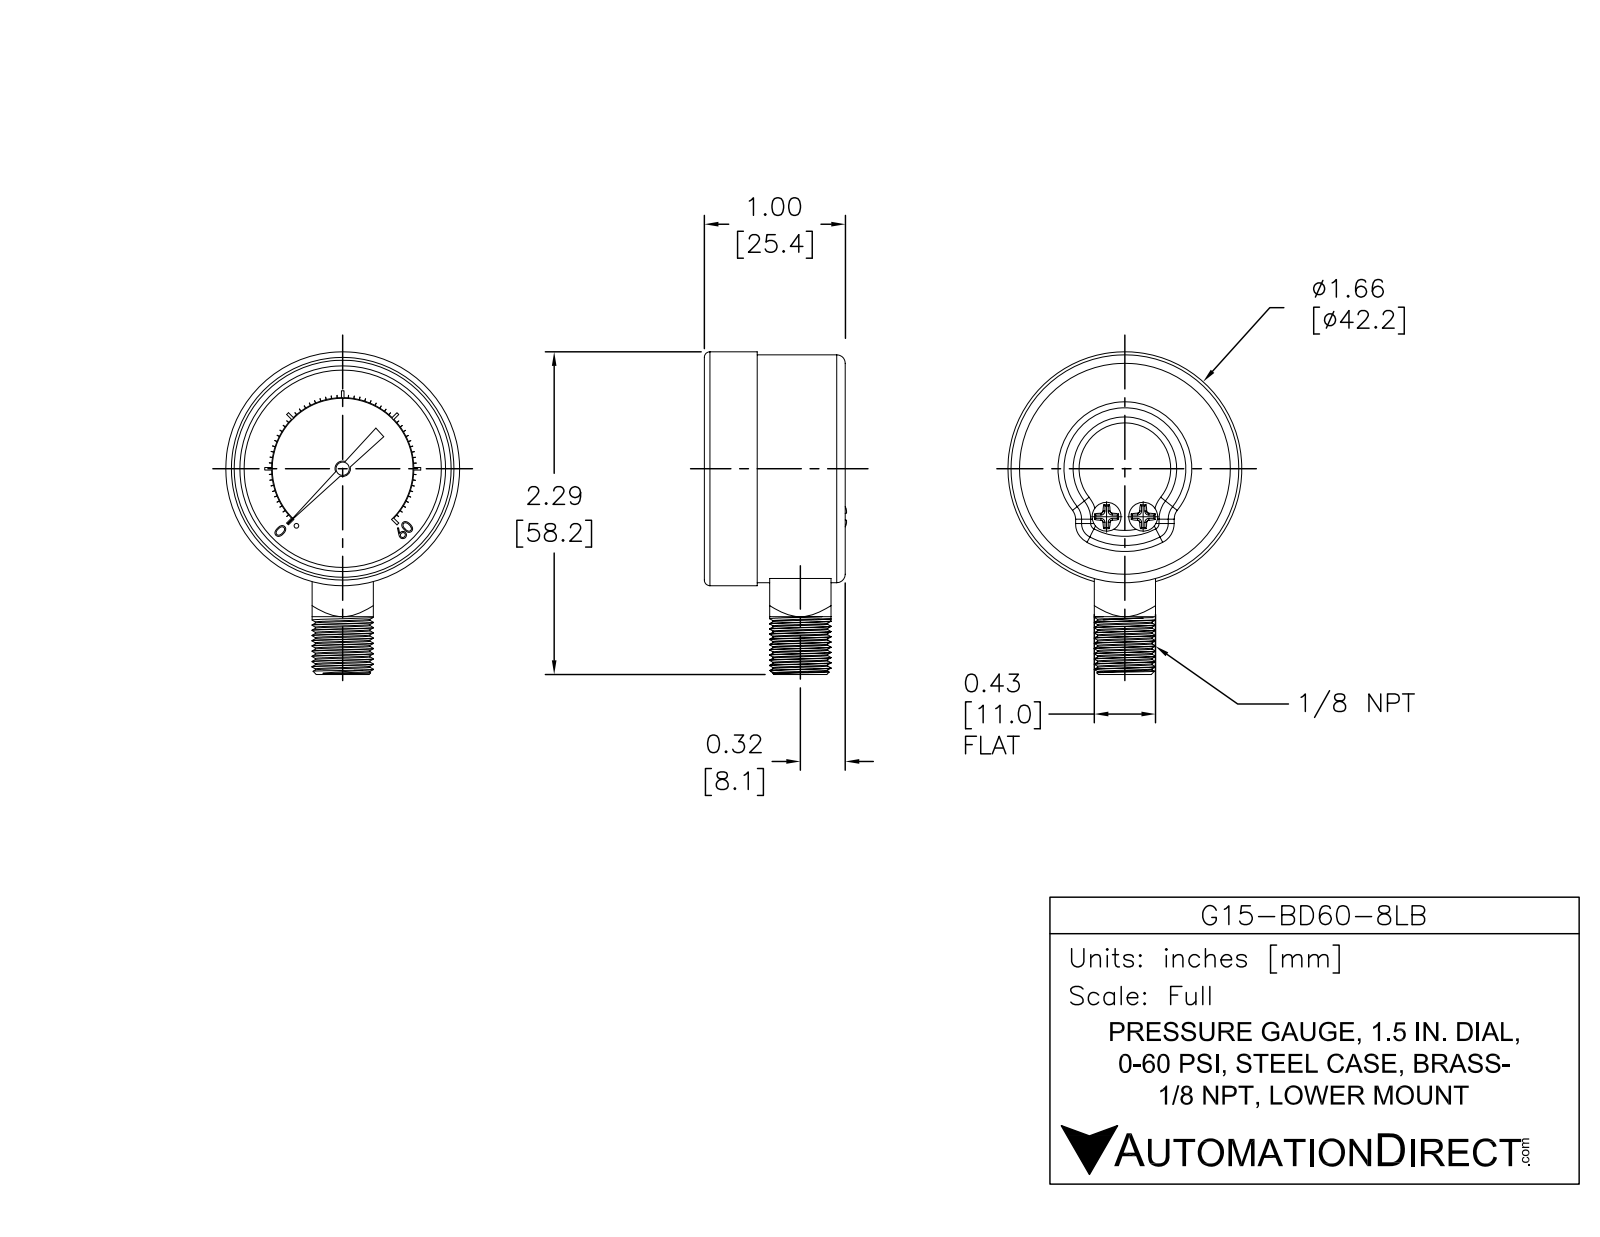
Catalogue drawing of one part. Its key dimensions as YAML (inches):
part_name: "G15-BD60-8LB"
step_written_by: "SolidWorks 2021 (AUTOMOTIVE_DESIGN)"
units: inches
bodies: {solids: 1, faces: 413, planar: 266, cylindrical: 82, other: 65}
overall_size: [2.29, 1.66, 1.01]
volume: 1.682
surface_area: 12.05
round_holes:
  - {diameter: 0.14, count: 1}
  - {diameter: 1.4, count: 1}
round_bosses_or_shafts:
  - {diameter: 0.205, count: 2}
  - {diameter: 1.66, count: 1}
  - {diameter: 1.617, count: 1}
  - {diameter: 0.435, count: 1}
  - {diameter: 0.11, count: 1}
  - {diameter: 0.095, count: 1}
  - {diameter: 0.033, count: 1}
partial_cylinders:
  - {radius: 0.06, count: 4}
  - {radius: 0.5, count: 1}
  - {radius: 0.505, count: 1}
face_to_face_distances: [0.71, 0.1, 0.61, 0.435, 0.96, 0.86, 0.25, 0.04, 0.625, 0.525]
